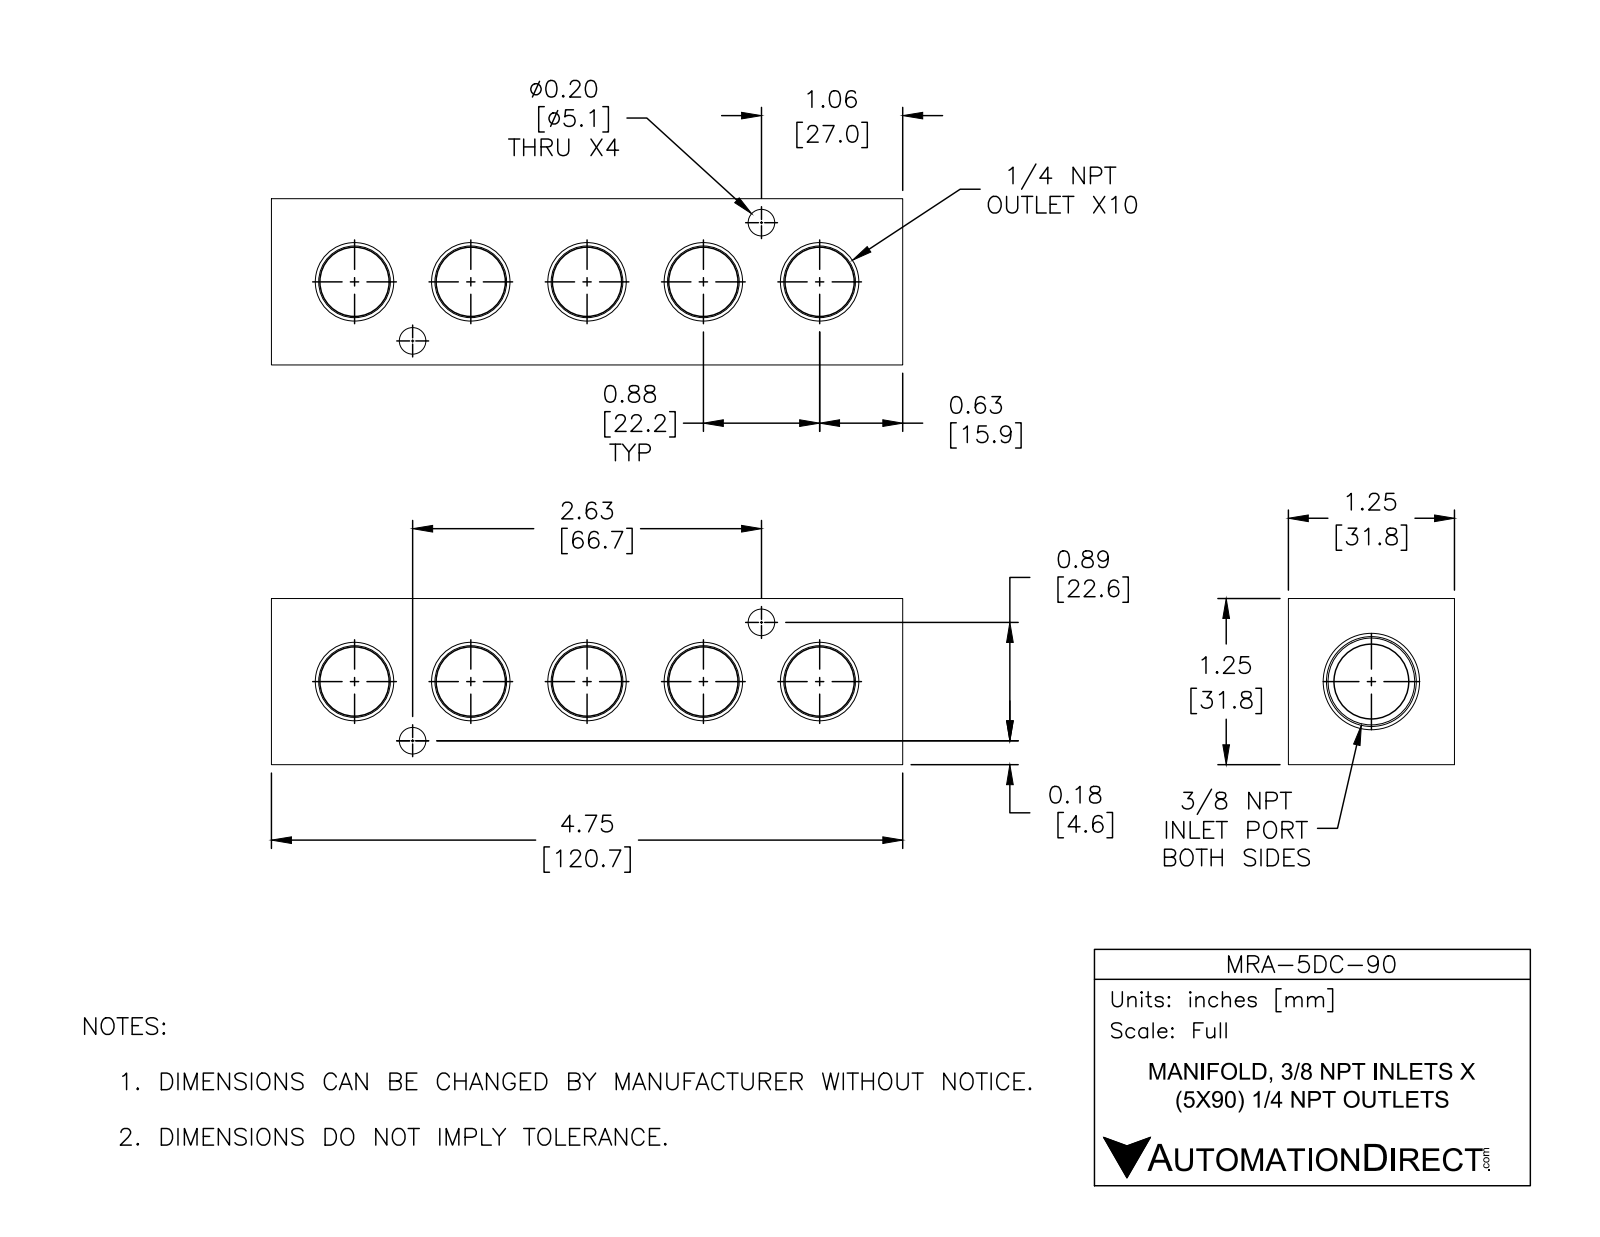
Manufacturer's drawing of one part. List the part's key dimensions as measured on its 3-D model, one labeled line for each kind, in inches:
Part name (STEP PRODUCT): MRA-5DC-90
STEP written by: SolidWorks 2015 (CONFIG_CONTROL_DESIGN)
Units: inches
Bodies: 1 solid, 118 faces (30 planar, 40 cylindrical, 48 other)
Overall size (bounding box): 4.75 × 1.25 × 1.25
Volume: 5.195 in³ · Surface area: 39.68 in²
Round holes (diameter × count): ⌀0.2 ×4, ⌀0.562 ×1
Partial cylindrical surfaces — rounded edges, fillets, slot ends (radius × count): R0.219 ×10
Main face-to-face distances: 1.25, 4.75, 0.86, 0.39, 0.41, 4.34, 3.93
Hole centre spacings: 2.772
